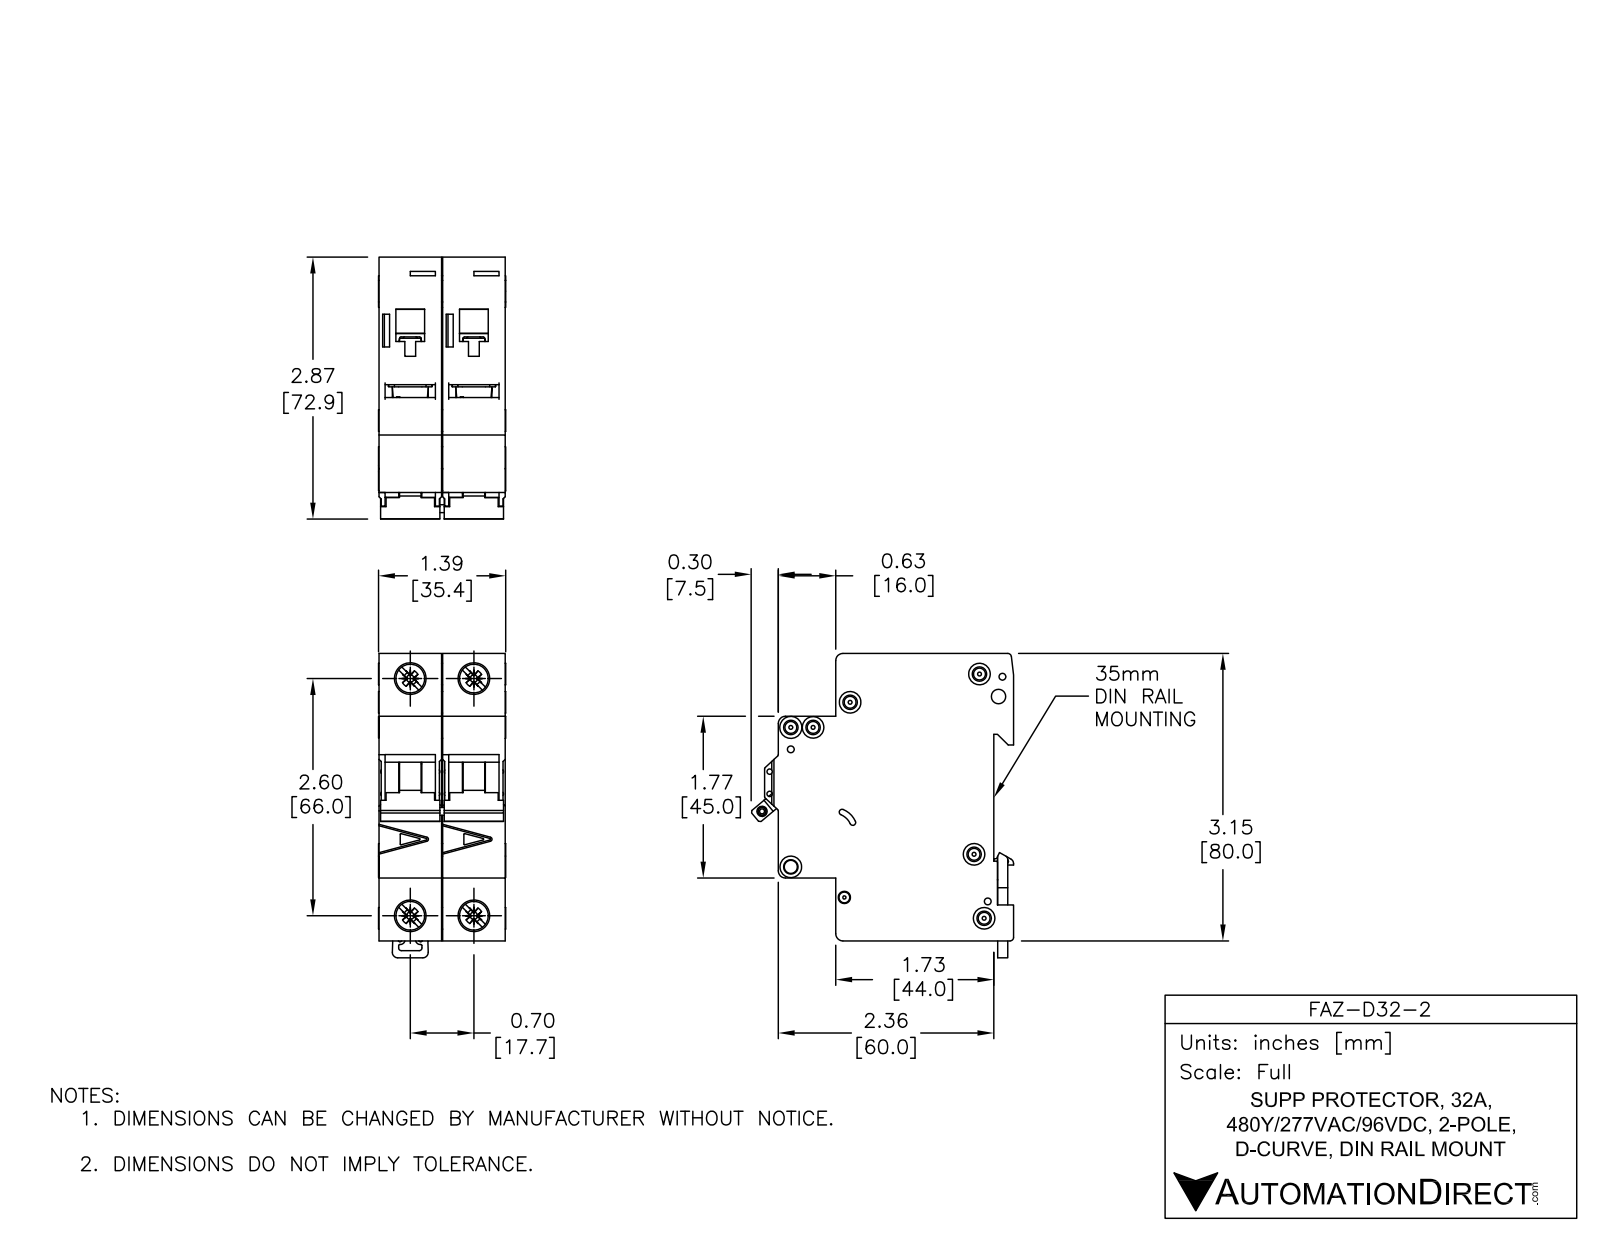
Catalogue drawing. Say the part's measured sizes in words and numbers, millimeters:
The part is named "FAZ-D32-2". Its 3-D file was written by "SolidWorks 2014 (AUTOMOTIVE_DESIGN)". It is 8 solids with 1104 faces: 466 planar, 396 cylindrical and 242 other. Overall it measures 84.78 by 73.04 by 35.4 millimeters. Its volume is 149 808 cubic millimeters and its surface area 38 799 square millimeters. Round holes: 6 of diameter 3.6, 3 of diameter 1.9, 2 of diameter 1.09, 2 of diameter 1.5, 2 of diameter 4, 2 of diameter 7.15, 2 of diameter 8.2, 1 of diameter 2.15, 1 of diameter 2.2, 1 of diameter 2.55, 1 of diameter 3.3, 1 of diameter 3.4. Round bosses or shafts: 4 of diameter 6, 2 of diameter 8.2, 2 of diameter 2.5. Partial cylindrical surfaces (rounded edges, fillets, slot ends): 49 of radius 0.25, 19 of radius 0.5, 10 of radius 2, 8 of radius 0.2, 8 of radius 1, 2 of radius 0.8, 2 of radius 1.8, 2 of radius 3. The main face-to-face distances are 17.7, 17.5, 35.2, 79.48, 5.5, 49.5, 44, 65.5, 60, 16. The hole center spacings are 6.2, 13.64, 17.7, 66, 68.33, 4.81, 5.19, 5.61.
